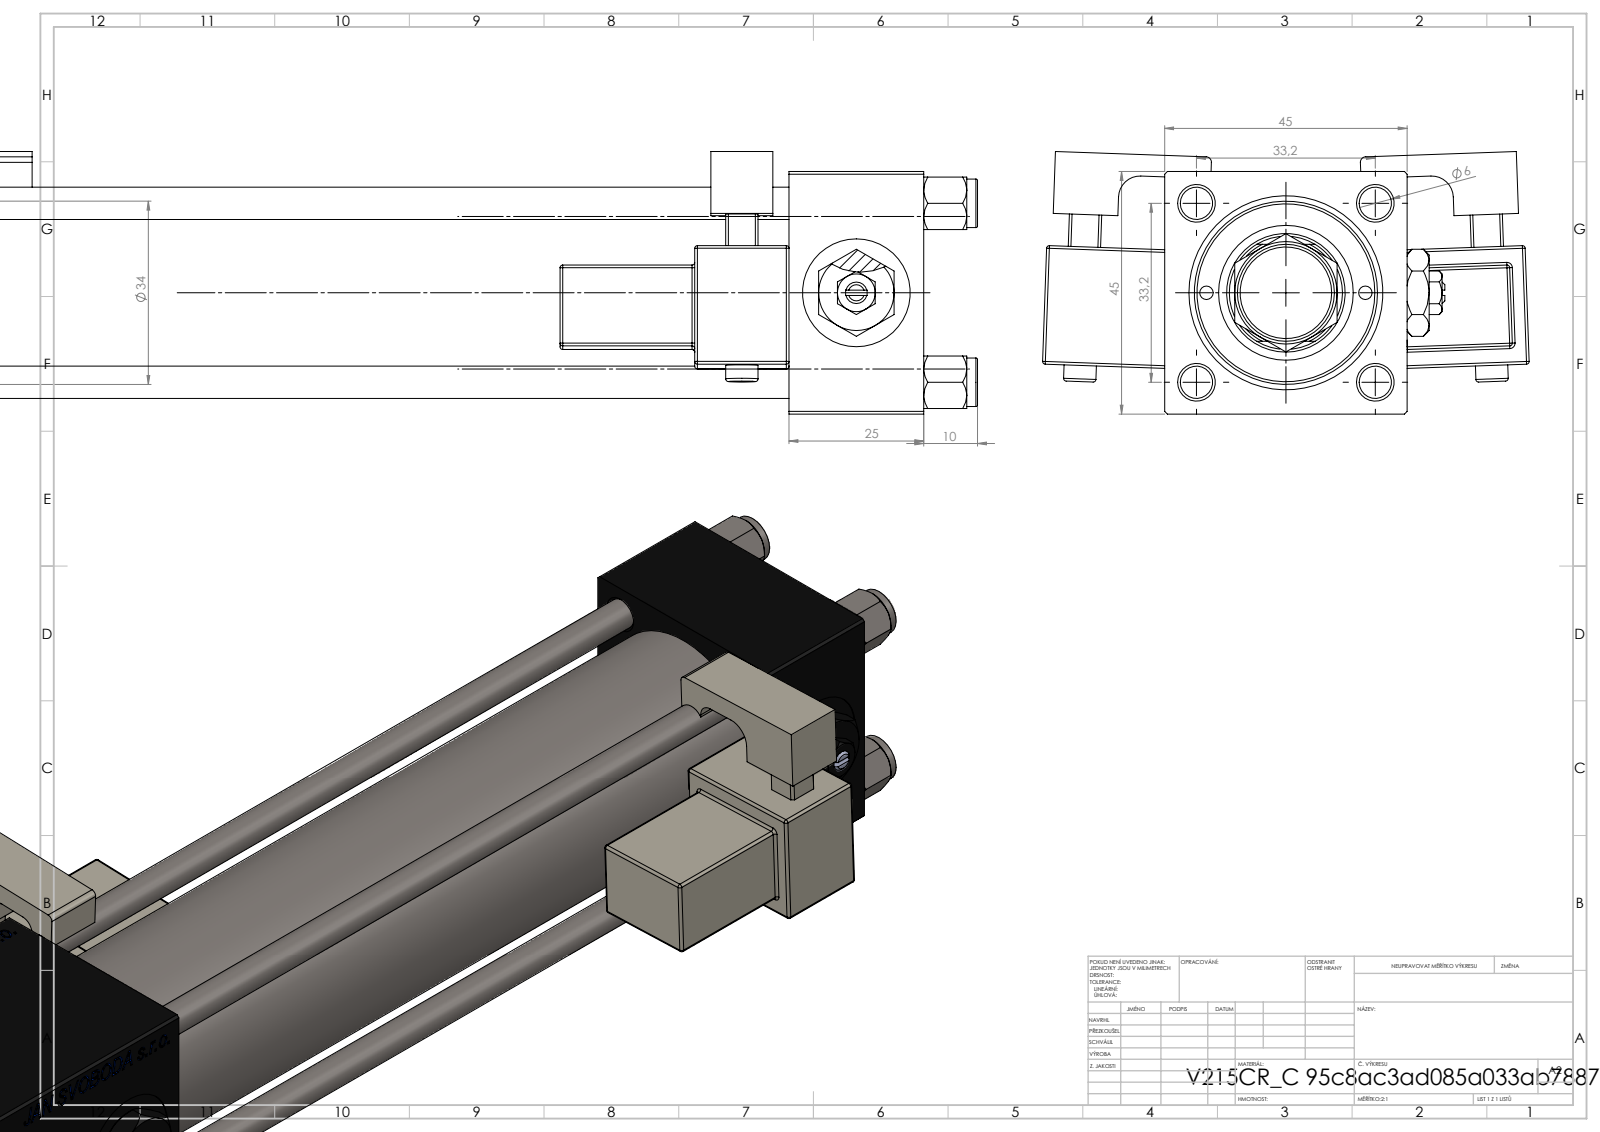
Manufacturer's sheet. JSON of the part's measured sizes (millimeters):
{"part_name": "V215CR_C_Body; V215CR_VCP_C; V215CR_C_TYCINKA; V215CR_MSU (+4 more)", "step_written_by": "SolidWorks 2019 (CONFIG_CONTROL_DESIGN)", "units": "millimeters", "bodies": {"solids": 16, "faces": 1464, "planar": 652, "cylindrical": 166, "other": 646}, "overall_size": [296, 90.31, 48.72], "volume_mm3": 343289, "surface_area_mm2": 126372, "round_holes": [[6, 4], [2.5, 2], [7, 2], [13.16, 2], [20, 2], [10.5, 1], [22, 1], [24, 1], [25, 1], [32, 1], [33, 1]], "round_bosses_or_shafts": [[9, 4], [6, 2], [38, 1], [34, 1], [18, 1], [11, 1]], "partial_cylinders_radius": [[0.5, 48], [1, 2], [2.5, 2], [4, 2], [10.5, 1]], "face_to_face_distances": [45, 25, 3, 180, 155, 228, 22.99, 137.5, 203, 44.8], "hole_center_spacings": [16.7, 23.48, 33.2, 35.47, 14.75, 46.95, 29.5, 180.5]}
